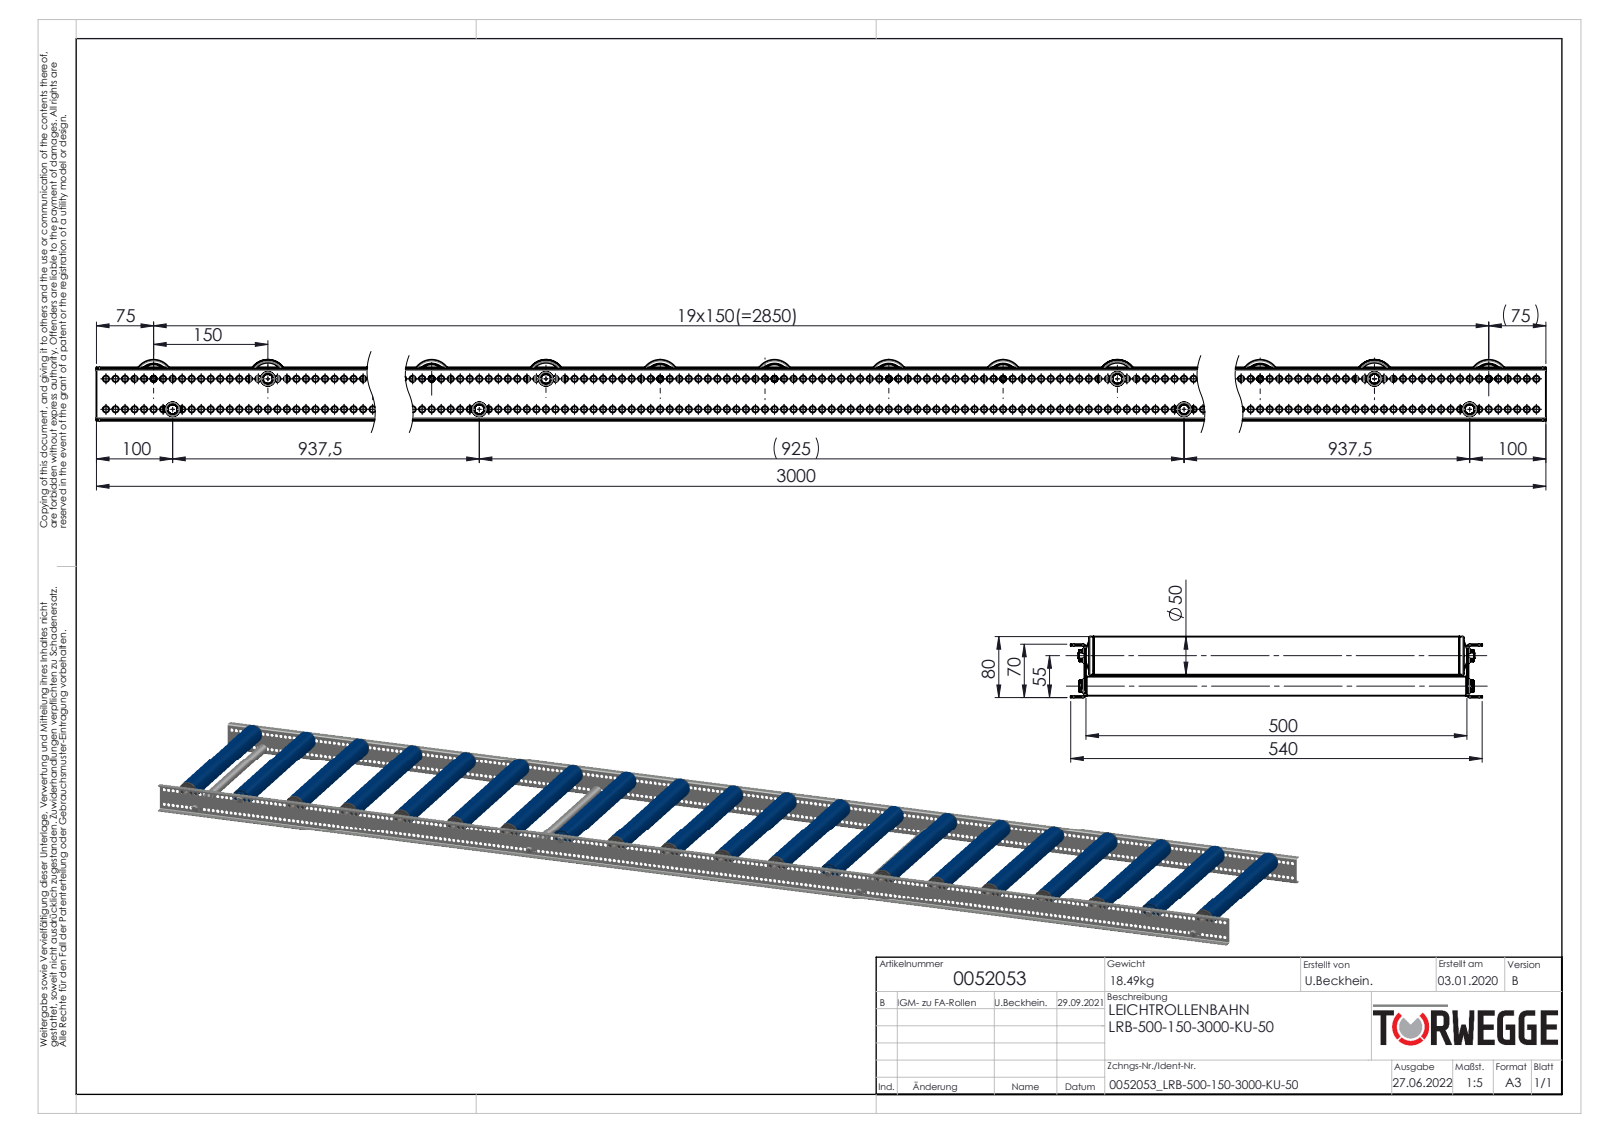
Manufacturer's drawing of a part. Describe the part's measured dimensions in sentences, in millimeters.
The part is named "Profil_LRB-20x70x20x2_KFG_S109080_U-PROFIL-20-70-20-2-LRB-L=3000; Traversen_KFG_L500; Druckfeder_1,2x10x30; 0026266_Typ-KUT100-50x2,8-12 (+8 more)". Its 3-D file was written by "SolidWorks 2020 (AUTOMOTIVE_DESIGN)". It is 414 solids with 8500 faces: 2012 planar, 3960 cylindrical and 2528 other. Overall it measures 3000 by 540 by 80 millimeters. Its volume is 7 173 000 cubic millimeters and its surface area 5 508 000 square millimeters. Round holes: 478 of diameter 8.2, 16 of diameter 7.6, 16 of diameter 8, 16 of diameter 25, 16 of diameter 30, 16 of diameter 35, 16 of diameter 39.4, 16 of diameter 40, 8 of diameter 6.8, 4 of diameter 12, 4 of diameter 12.1, 4 of diameter 16. Round bosses or shafts: 20 of diameter 50, 16 of diameter 44.4, 16 of diameter 38, 16 of diameter 36, 16 of diameter 33, 16 of diameter 22, 16 of diameter 21, 8 of diameter 25. Partial cylindrical surfaces (rounded edges, fillets, slot ends): 32 of radius 0.6, 32 of radius 0.75, 32 of radius 2.45, 16 of radius 2.5, 16 of radius 4.87, 16 of radius 7, 8 of radius 4, 4 of radius 2. The main face-to-face distances are 2, 502, 68, 500, 504, 70, 66, 6, 492, 12. The hole center spacings are 12.5, 25, 37.5, 50, 62.5, 75, 87.5, 100.
